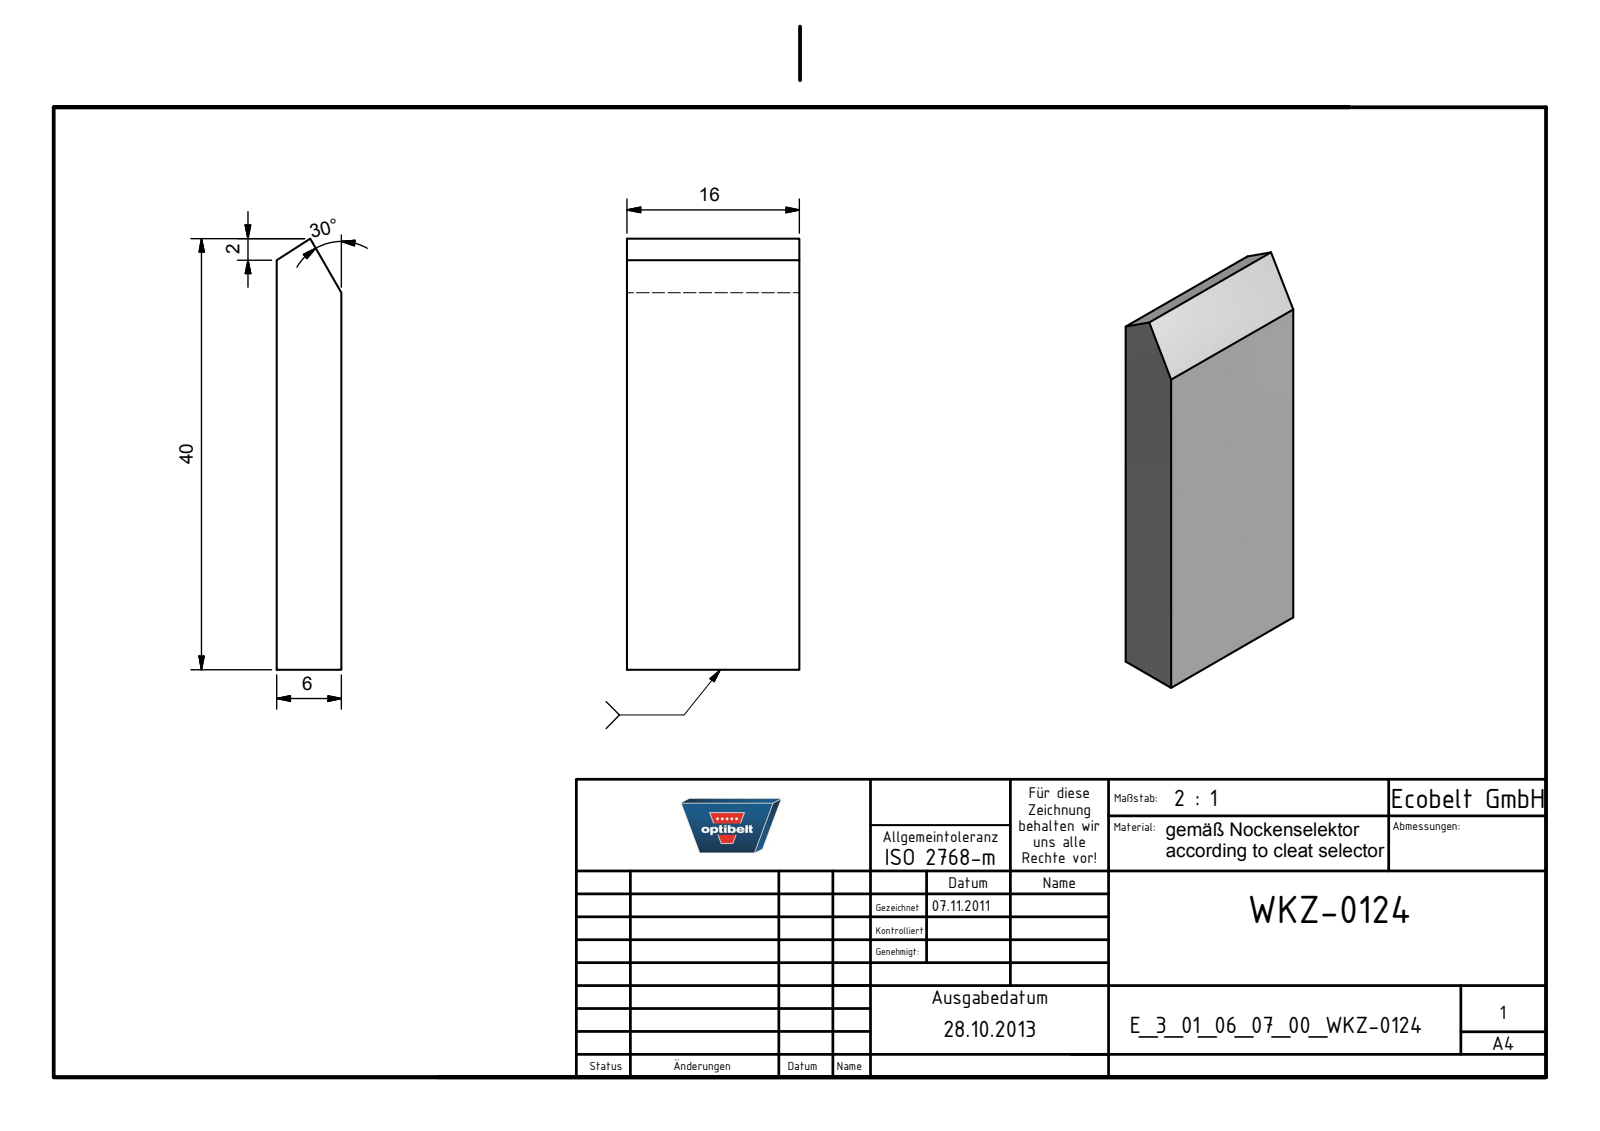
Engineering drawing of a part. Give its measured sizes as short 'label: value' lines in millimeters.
name: E_3_01_06_07_00_WKZ-0124
written by: Autodesk Inventor 2025 (AUTOMOTIVE_DESIGN)
unit: mm
bodies: 1 solid, 7 faces (7 planar, 0 cylindrical, 0 other)
size: 40 × 16 × 6
volume: 3 674 mm³; area: 1 875 mm²
face distances: 6, 16
